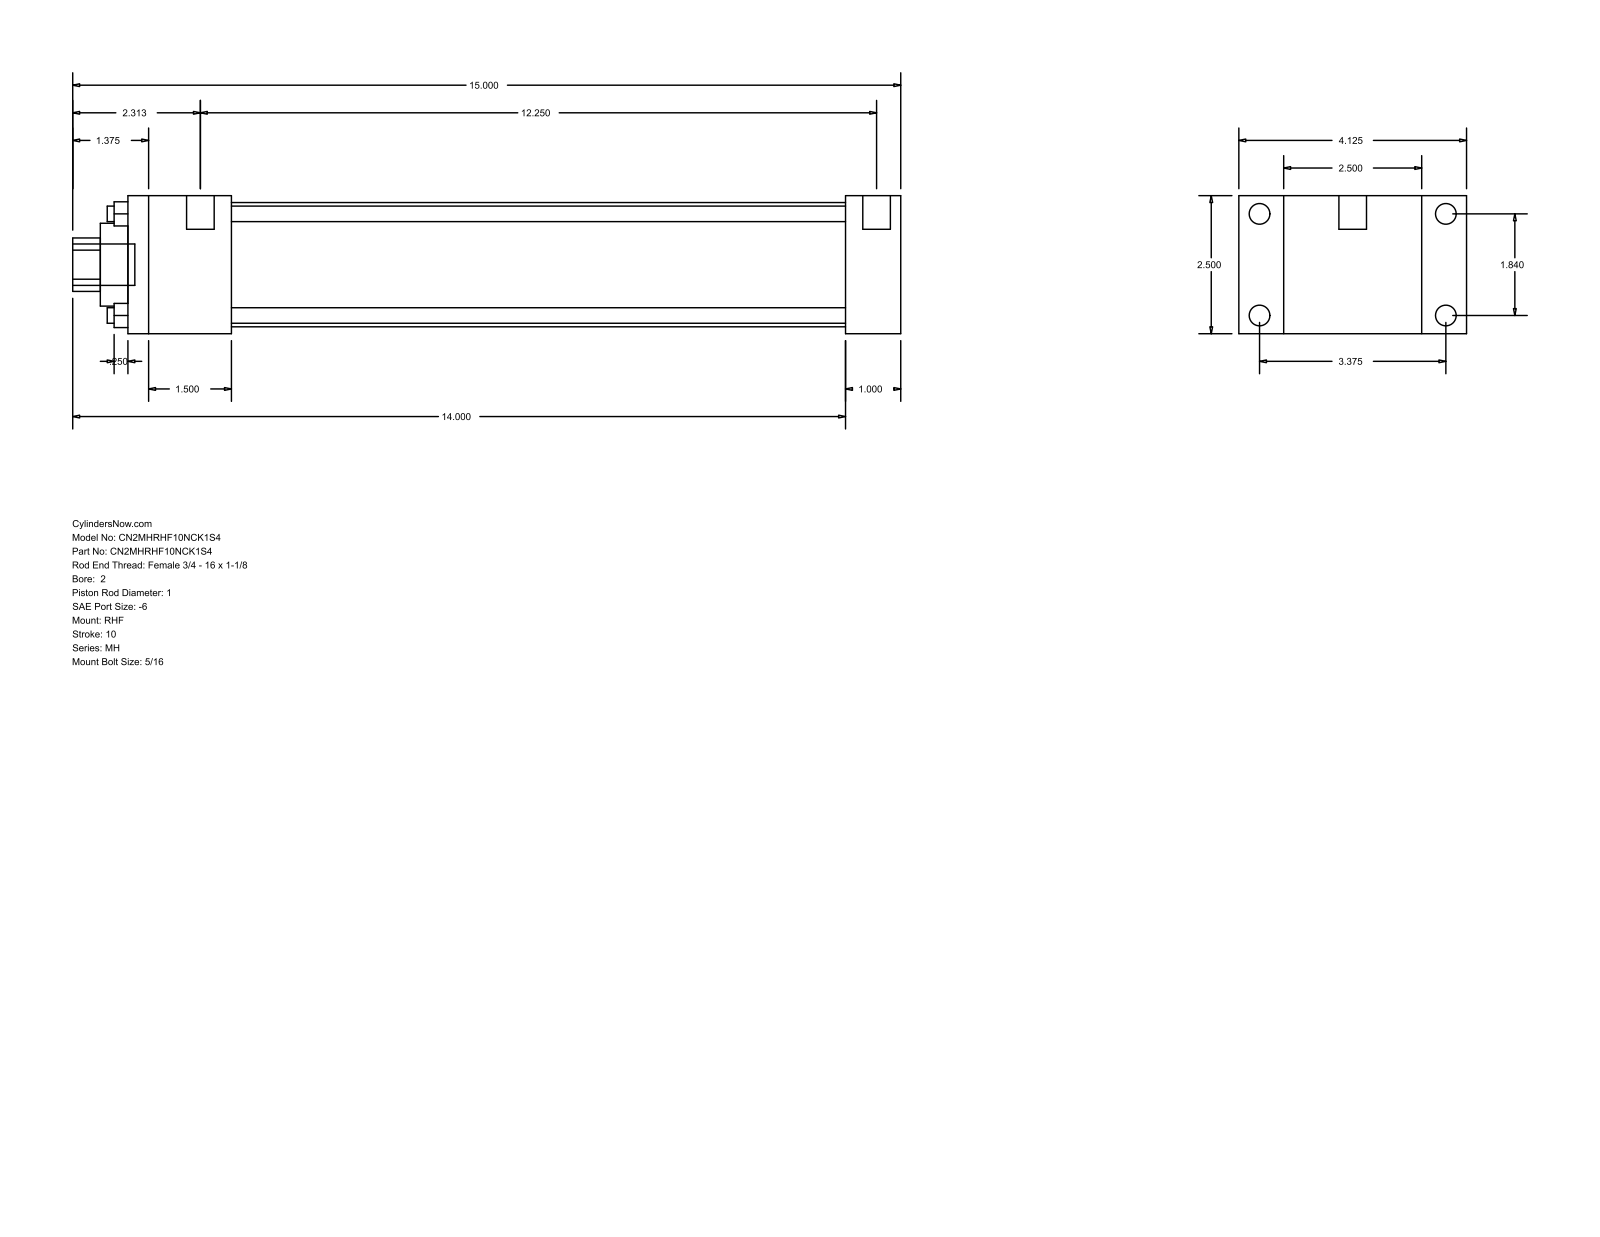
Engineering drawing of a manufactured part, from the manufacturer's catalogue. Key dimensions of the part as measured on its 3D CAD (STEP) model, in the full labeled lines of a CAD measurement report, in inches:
Part name (STEP PRODUCT): MH_RHF__0200_1
STEP written by: GSSL Pune (CONFIG_CONTROL_DESIGN)
Units: inches
Bodies: 0 solids, 88 faces (60 planar, 28 cylindrical, 0 other)
Overall size (bounding box): 15 × 4.125 × 2.5
Round holes (diameter × count): ⌀0.281 ×4, ⌀1 ×1, ⌀1.5 ×1, ⌀2.25 ×1
Round bosses / shafts (diameter × count): ⌀0.375 ×4, ⌀0.219 ×4, ⌀0.5 ×2, ⌀0.75 ×1
Partial cylindrical surfaces — rounded edges, fillets, slot ends (radius × count): R0.484 ×1
Main face-to-face distances: 2.5, 1, 0.813, 3.313, 14, 13, 4.125, 1.875, 11.125, 12.125
Hole centre spacings: 1.301, 1.84, 2.602
